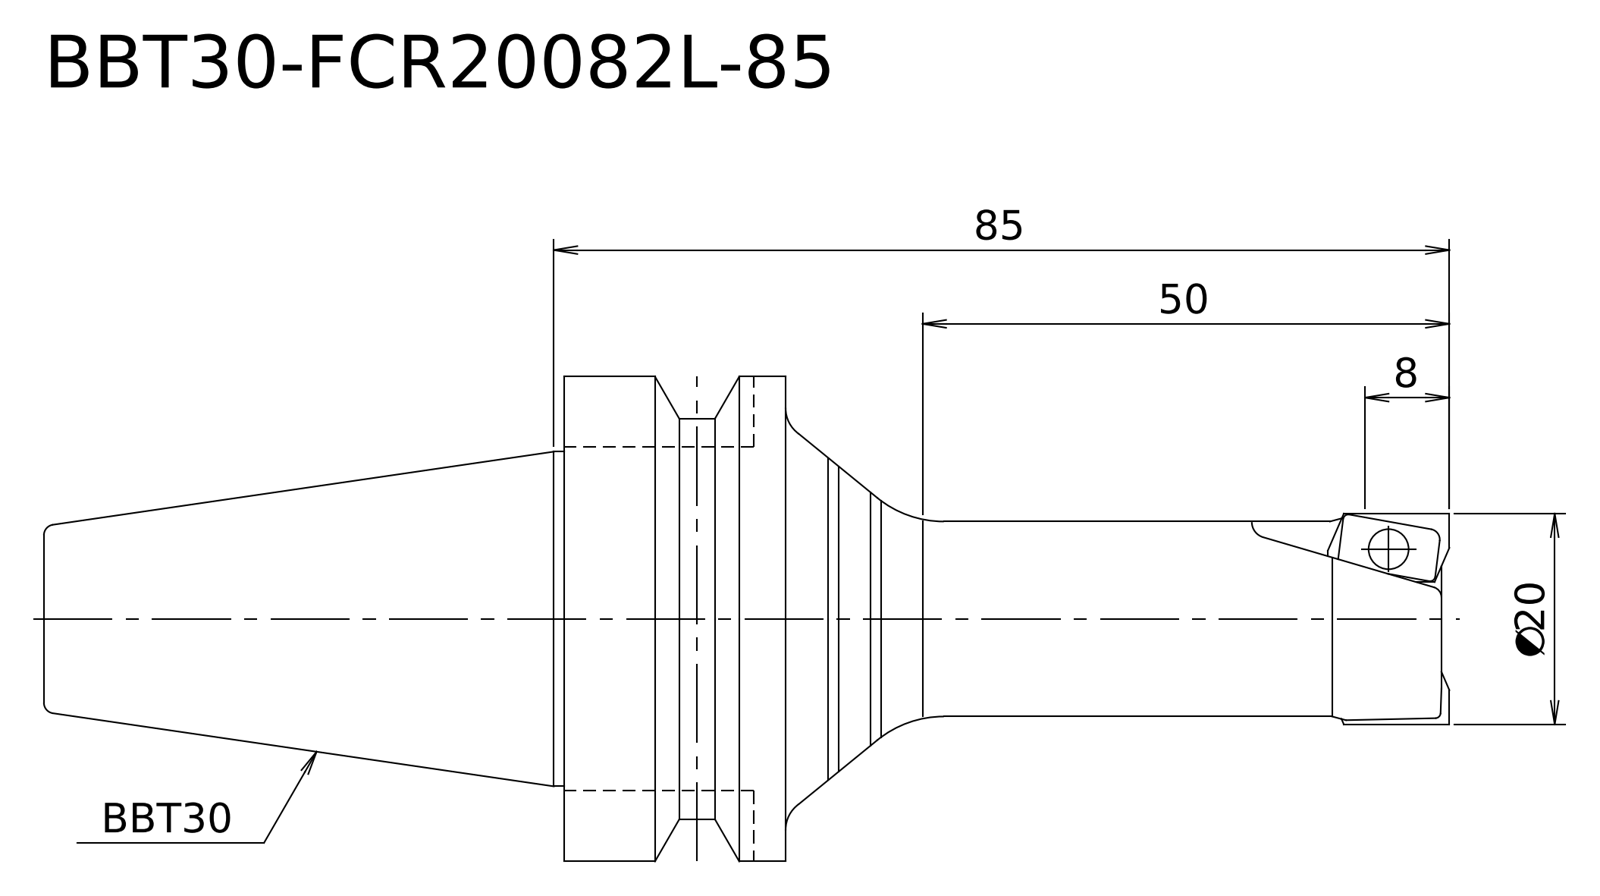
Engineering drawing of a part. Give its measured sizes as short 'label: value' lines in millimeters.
written by: Kubotek KeyCreator V8.5.1 (14335) (CONFIG_CONTROL_DESIGN)
unit: mm
bodies: 1 solid, 17 faces (4 planar, 6 cylindrical, 7 other)
size: 133.4 × 46 × 46
volume: 78 301 mm³; area: 13 704 mm²
bosses: 1× ⌀46, 1× ⌀38, 1× ⌀31.75, 1× ⌀20, 1× ⌀18.5
face distances: 21, 63, 84, 133.4, 70.4, 49.4
